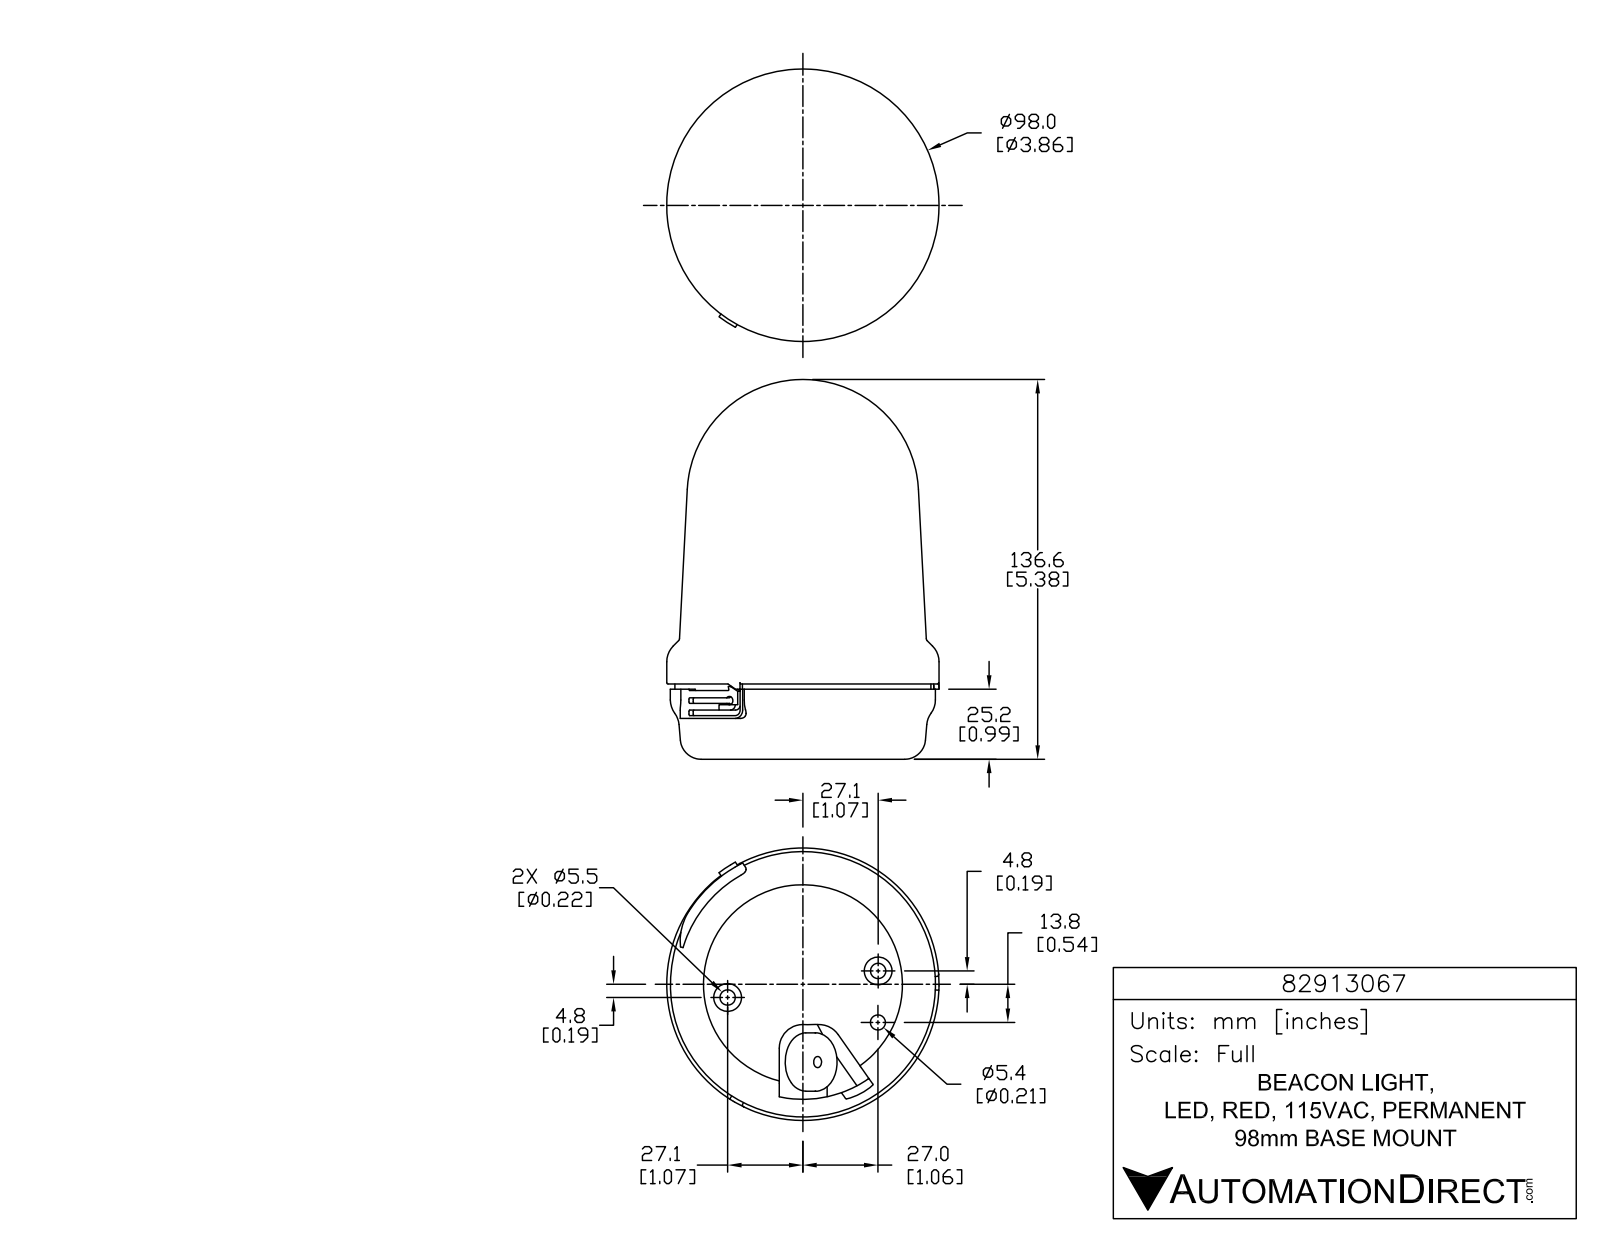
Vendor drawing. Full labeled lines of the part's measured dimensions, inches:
Part name (STEP PRODUCT): 82913067
STEP written by: SolidWorks 2015 (AUTOMOTIVE_DESIGN)
Units: inches
Bodies: 1 solid, 872 faces (566 planar, 204 cylindrical, 102 other)
Overall size (bounding box): 5.378 × 3.858 × 3.858
Volume: 44.69 in³ · Surface area: 73.66 in²
Round holes (diameter × count): ⌀0.059 ×3, ⌀0.217 ×2, ⌀0.157 ×1, ⌀0.213 ×1, ⌀2.819 ×1
Round bosses / shafts (diameter × count): ⌀0.339 ×3, ⌀0.084 ×3, ⌀0.394 ×2, ⌀3.858 ×1, ⌀3.756 ×1, ⌀3.626 ×1, ⌀0.827 ×1
Partial cylindrical surfaces — rounded edges, fillets, slot ends (radius × count): R0.005 ×9, R0.005 ×6, R0.012 ×6, R0.012 ×6, R0.012 ×6, R0.196 ×6, R0.02 ×5, R0.039 ×4
Main face-to-face distances: 1.045, 0.972, 0.073, 0.02, 0.992, 1.065, 0.236, 0.579, 0.559, 0.413
Hole centre spacings: 1.083, 0.73, 1.193, 2.158, 2.165
